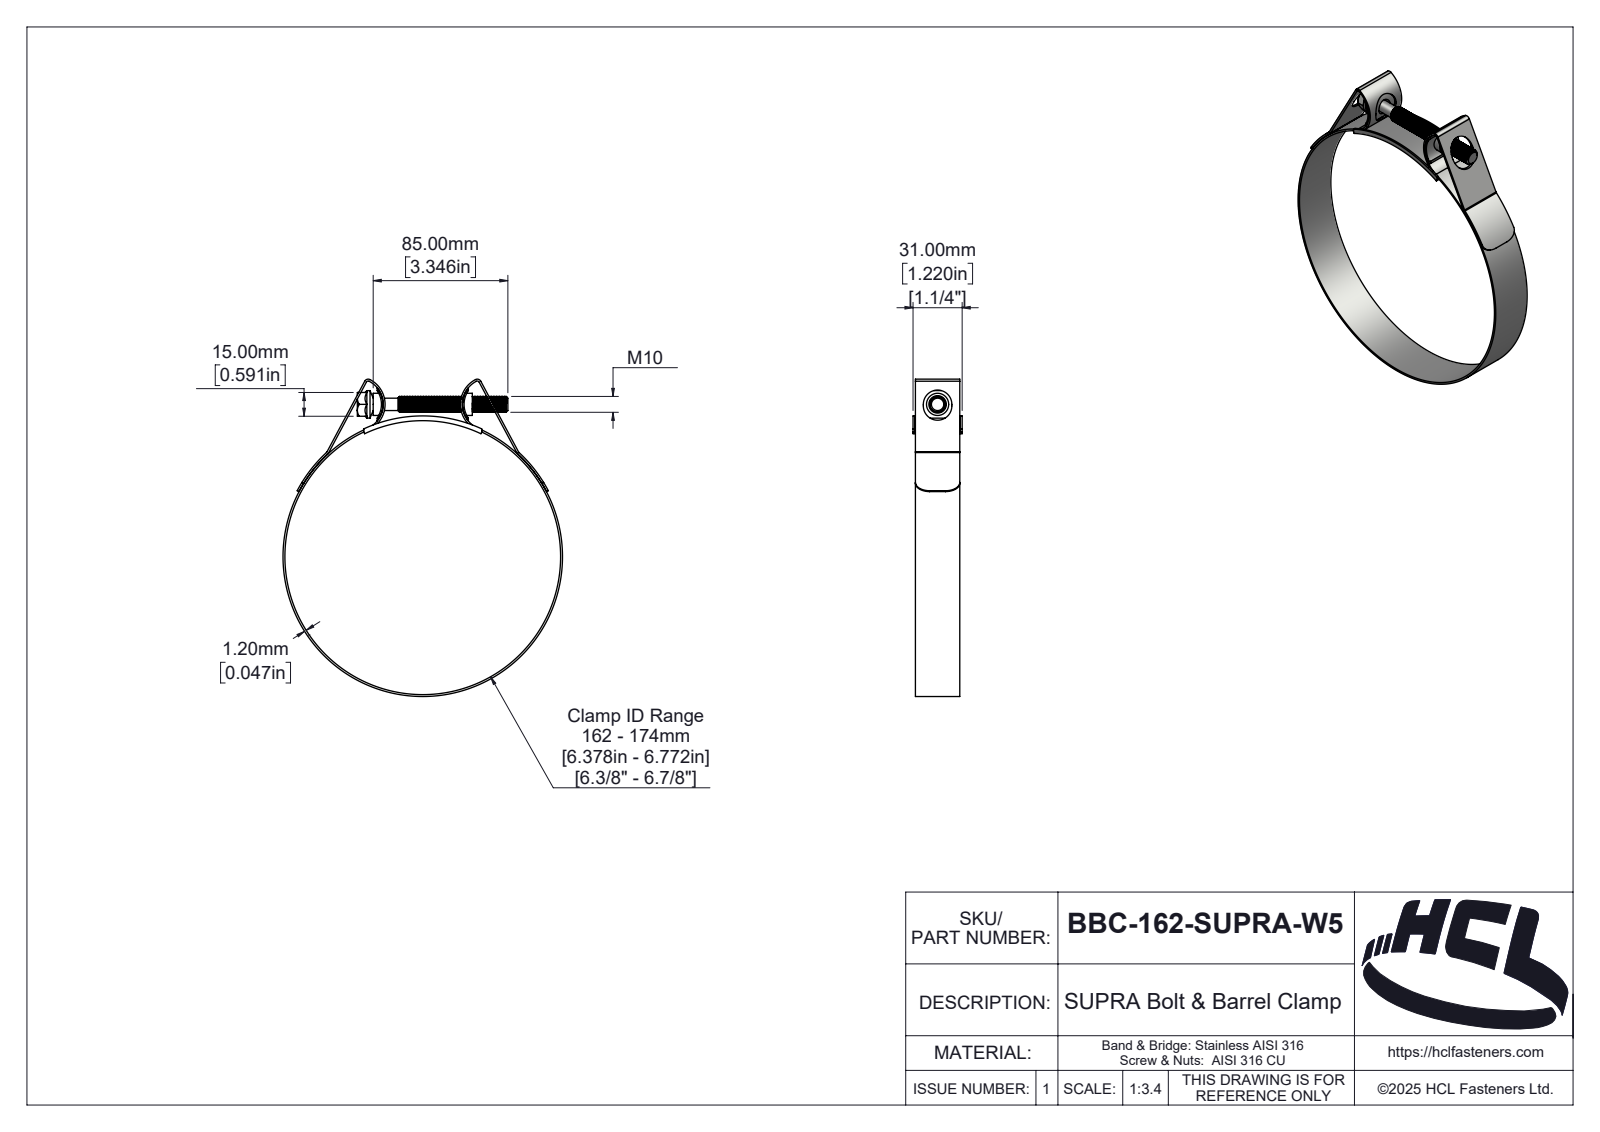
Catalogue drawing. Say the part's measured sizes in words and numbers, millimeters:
The part is named "BBC-162-SUPRA-W5". Its 3-D file was written by "SolidWorks 2025 (AUTOMOTIVE_DESIGN)". It is 5 solids with 379 faces: 46 planar, 247 cylindrical and 86 other. Overall it measures 200.2 by 176.4 by 31 millimeters. Its volume is 35 253 cubic millimeters and its surface area 53 324 square millimeters. Round holes: 1 of diameter 174. Round bosses or shafts: 1 of diameter 176.4, 1 of diameter 17.32, 1 of diameter 14, 1 of diameter 10, 1 of diameter 7.8. Partial cylindrical surfaces (rounded edges, fillets, slot ends): 4 of radius 1, 2 of radius 1.3, 2 of radius 2, 2 of radius 2.5, 2 of radius 3.2, 2 of radius 9, 2 of radius 15.32, 2 of radius 16.32. The main face-to-face distances are 1.2, 28, 1.5, 29.5, 29.8, 28.3, 31, 28.6, 15, 2.5.
